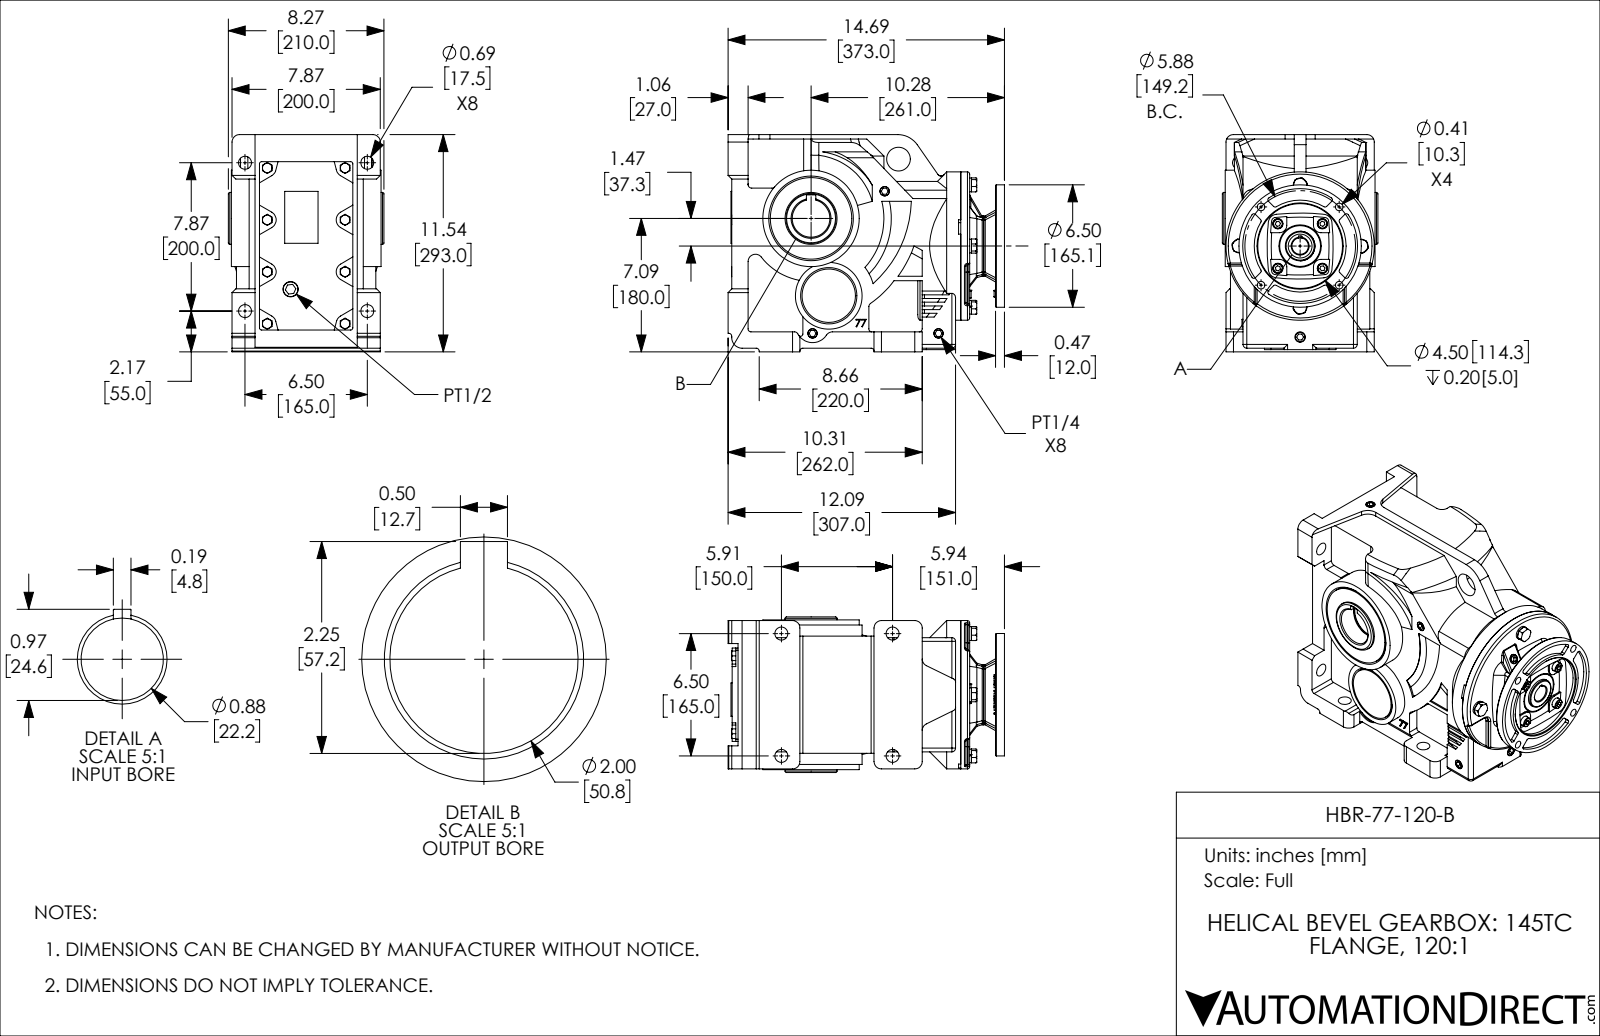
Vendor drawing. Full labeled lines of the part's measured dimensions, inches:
Part name (STEP PRODUCT): HBR-77-120-B
STEP written by: SolidWorks 2018 (AUTOMOTIVE_DESIGN)
Units: inches
Bodies: 44 solids, 2018 faces (886 planar, 704 cylindrical, 428 other)
Overall size (bounding box): 14.685 × 11.535 × 8.268
Volume: 321 in³ · Surface area: 1 848 in²
Round holes (diameter × count): ⌀0.268 ×12, ⌀0.354 ×12, ⌀0.689 ×8, ⌀0.315 ×4, ⌀0.335 ×4, ⌀0.402 ×4, ⌀0.406 ×4, ⌀0.433 ×4, ⌀0.551 ×4, ⌀0.438 ×3, ⌀0.118 ×2, ⌀0.487 ×2
Round bosses / shafts (diameter × count): ⌀0.315 ×8, ⌀0.724 ×4, ⌀0.512 ×4, ⌀0.394 ×4, ⌀7.874 ×1, ⌀6.5 ×1, ⌀5.118 ×1, ⌀3.543 ×1
Partial cylindrical surfaces — rounded edges, fillets, slot ends (radius × count): R0.394 ×40, R0.177 ×24, R0.118 ×23, R0.197 ×12, R0.315 ×12, R0.079 ×11, R0.157 ×11, R0.472 ×10
Main face-to-face distances: 0.236, 0.472, 0.315, 4.961, 0.276, 0.787, 0.512, 5.748, 0.551, 5.276
Hole centre spacings: 2.384, 5.716, 2.38, 2.756, 4.968, 6.496, 1.673, 2.937
